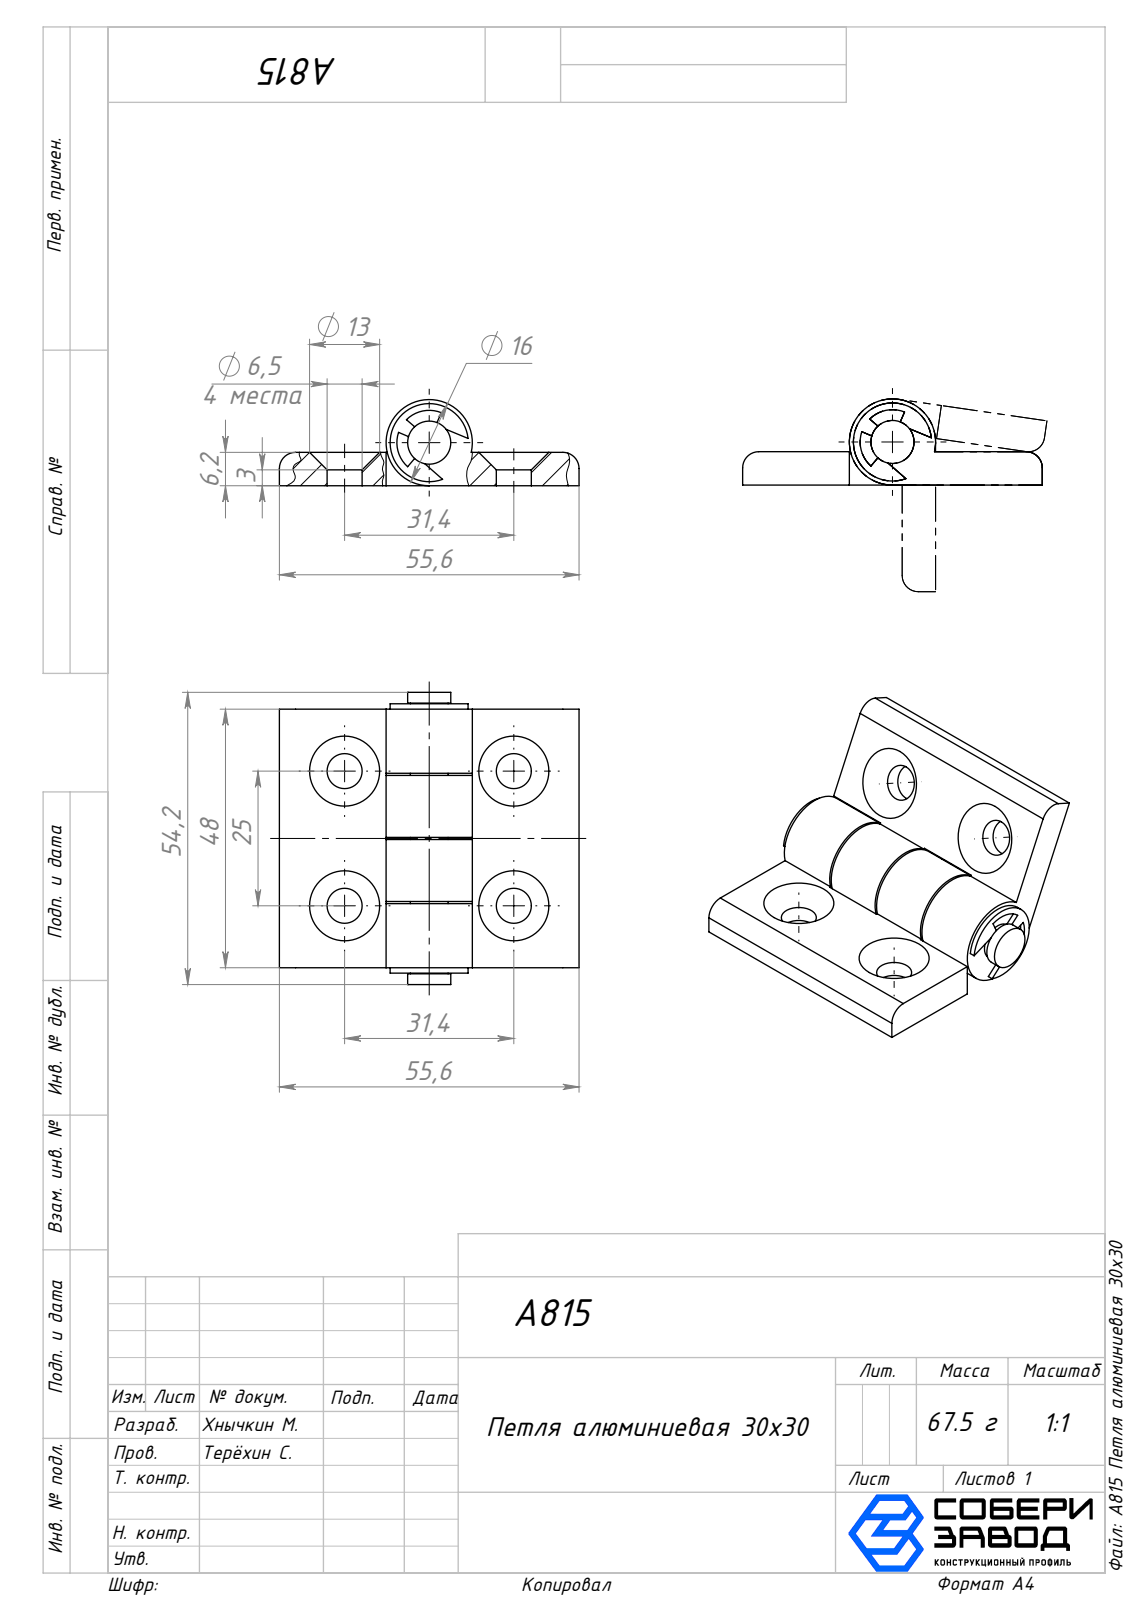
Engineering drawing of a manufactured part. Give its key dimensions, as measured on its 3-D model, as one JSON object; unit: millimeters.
{"part_name": "A815 Кольцо_00; A815 Петля алюминиевая 30x30; A815 Палец_01; A815 Петля, часть 30 серии_00", "step_written_by": "SolidWorks 2025 (AUTOMOTIVE_DESIGN)", "units": "millimeters", "bodies": {"solids": 5, "faces": 98, "planar": 40, "cylindrical": 50, "other": 8}, "overall_size": [55.59, 54.25, 16], "volume_mm3": 20707, "surface_area_mm2": 11608, "round_holes": [[6.5, 4], [7, 1]], "round_bosses_or_shafts": [[16, 1], [8, 1]], "partial_cylinders_radius": [[3, 2], [6, 1], [7.25, 1]], "face_to_face_distances": [6.2, 11.9, 12.3, 23.8, 24.2, 0.4, 48, 35.7, 36.1, 11.5], "hole_center_spacings": [25, 31.39, 40.13]}
